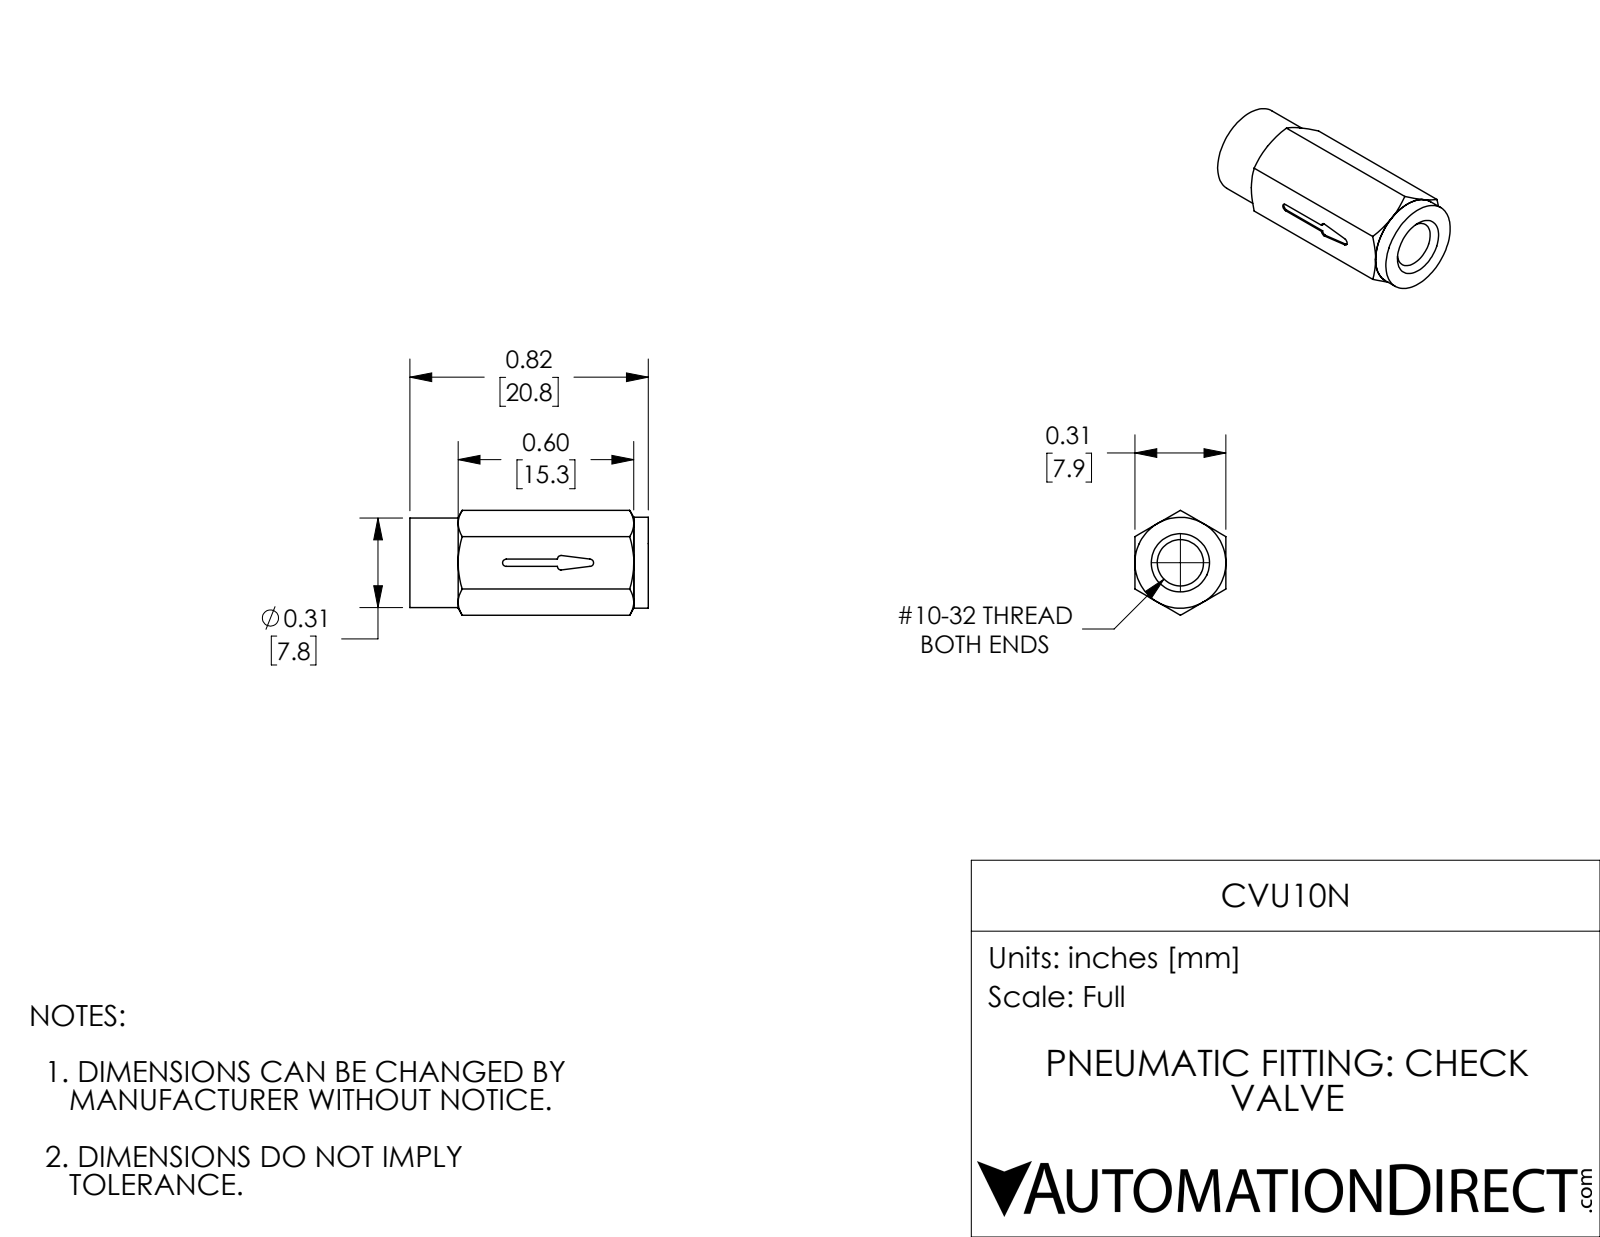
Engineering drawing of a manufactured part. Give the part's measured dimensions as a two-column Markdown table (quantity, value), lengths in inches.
| quantity | value |
| --- | --- |
| part name | CVU10N |
| STEP written by | SolidWorks 2018 (AUTOMOTIVE_DESIGN) |
| units | inches |
| bodies | 2 solids, 52 faces (18 planar, 16 cylindrical, 18 other) |
| overall size | 0.82 × 0.361 × 0.313 |
| volume | 0.039 in³ |
| surface area | 1.939 in² |
| round holes (diameter × count) | 0.159 × 1, 0.25 × 1 |
| round bosses / shafts (diameter × count) | 0.313 × 1, 0.308 × 1, 0.258 × 1 |
| partial cylindrical surfaces (radius × count) | 0.012 × 4 |
| main face-to-face distances | 0.313, 0.05, 0.77, 0.82, 0.572, 0.198, 0.248, 0.145, 0.427, 0.625 |
